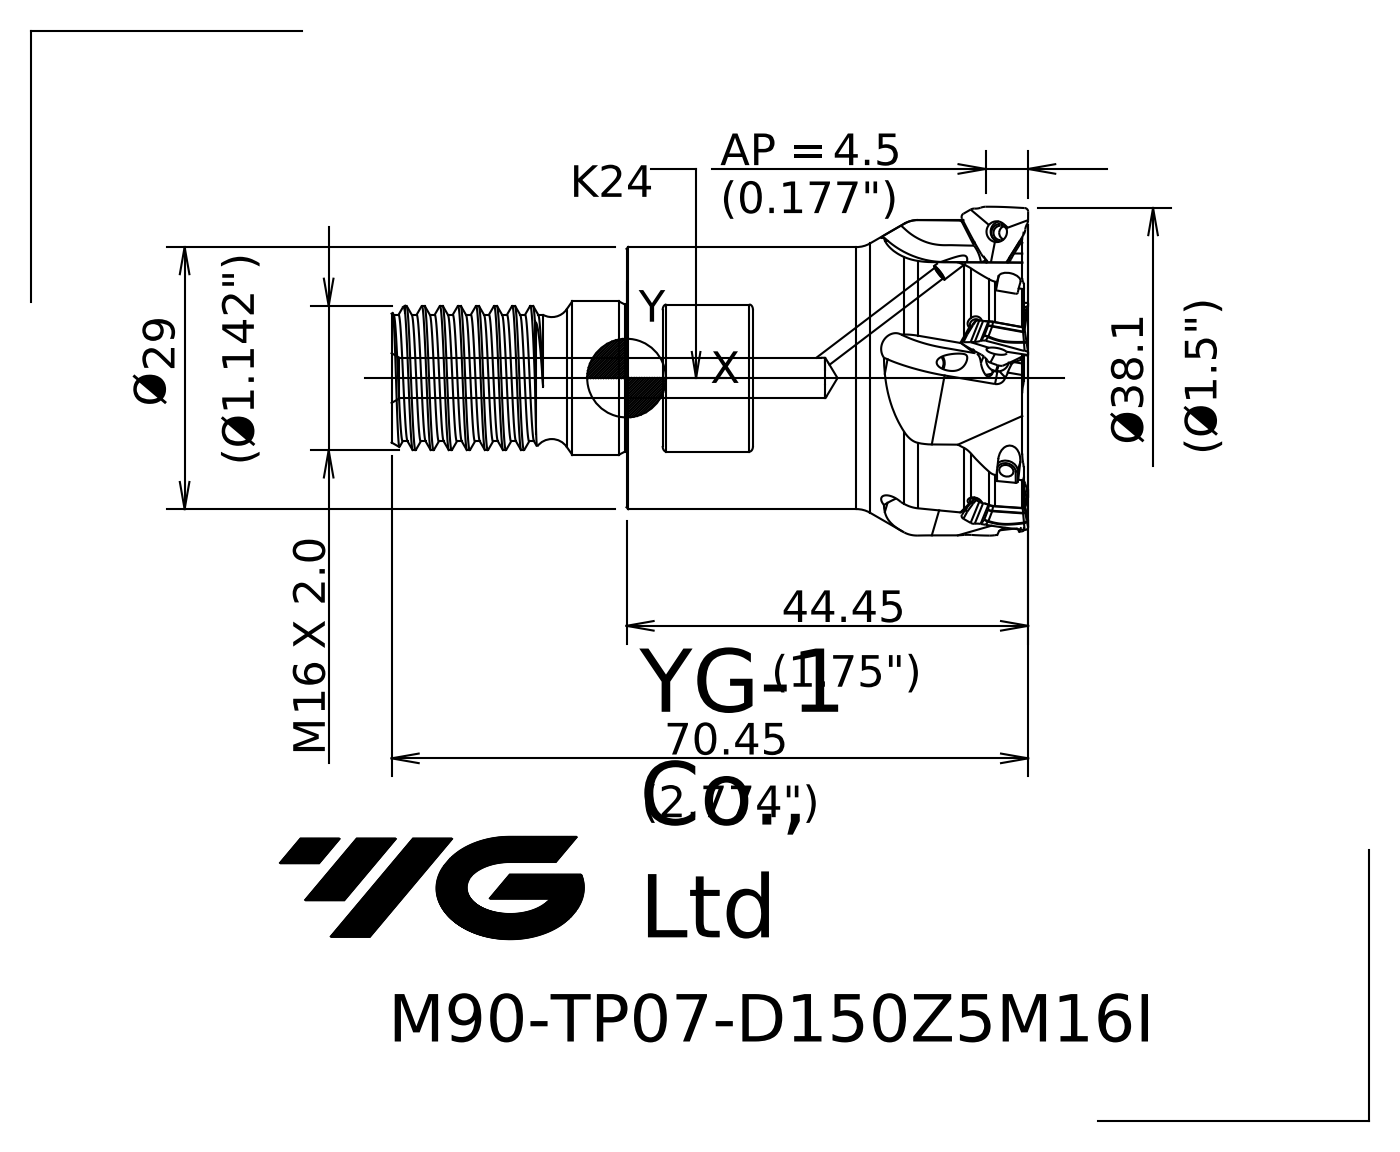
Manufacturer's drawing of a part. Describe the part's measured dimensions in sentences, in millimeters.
The part is named "10226C64D2E166g3". Its 3-D file was written by "SIEMENS PLM Software NX 10.0 (AP203_CONFIGURATION_CONTROLLED_3D_DESIGN_OF_MECHANICAL_PARTS_AND_ASSEMBLIES_MIM_LF)". It is 1 solid with 67 faces: 11 planar, 11 cylindrical and 45 other. Overall it measures 70.45 by 38.16 by 38.16 millimeters. Its volume is 37 191 cubic millimeters and its surface area 10 851 square millimeters. Round holes: 1 of diameter 1.5, 1 of diameter 4.5. Round bosses or shafts: 1 of diameter 35, 1 of diameter 29, 1 of diameter 17, 1 of diameter 16, 1 of diameter 14. Partial cylindrical surfaces (rounded edges, fillets, slot ends): 4 of radius 0.4. The main face-to-face distances are 43.8, 24, 69.8, 26, 43.95, 69.95, 39.95, 39.8, 4, 30.
